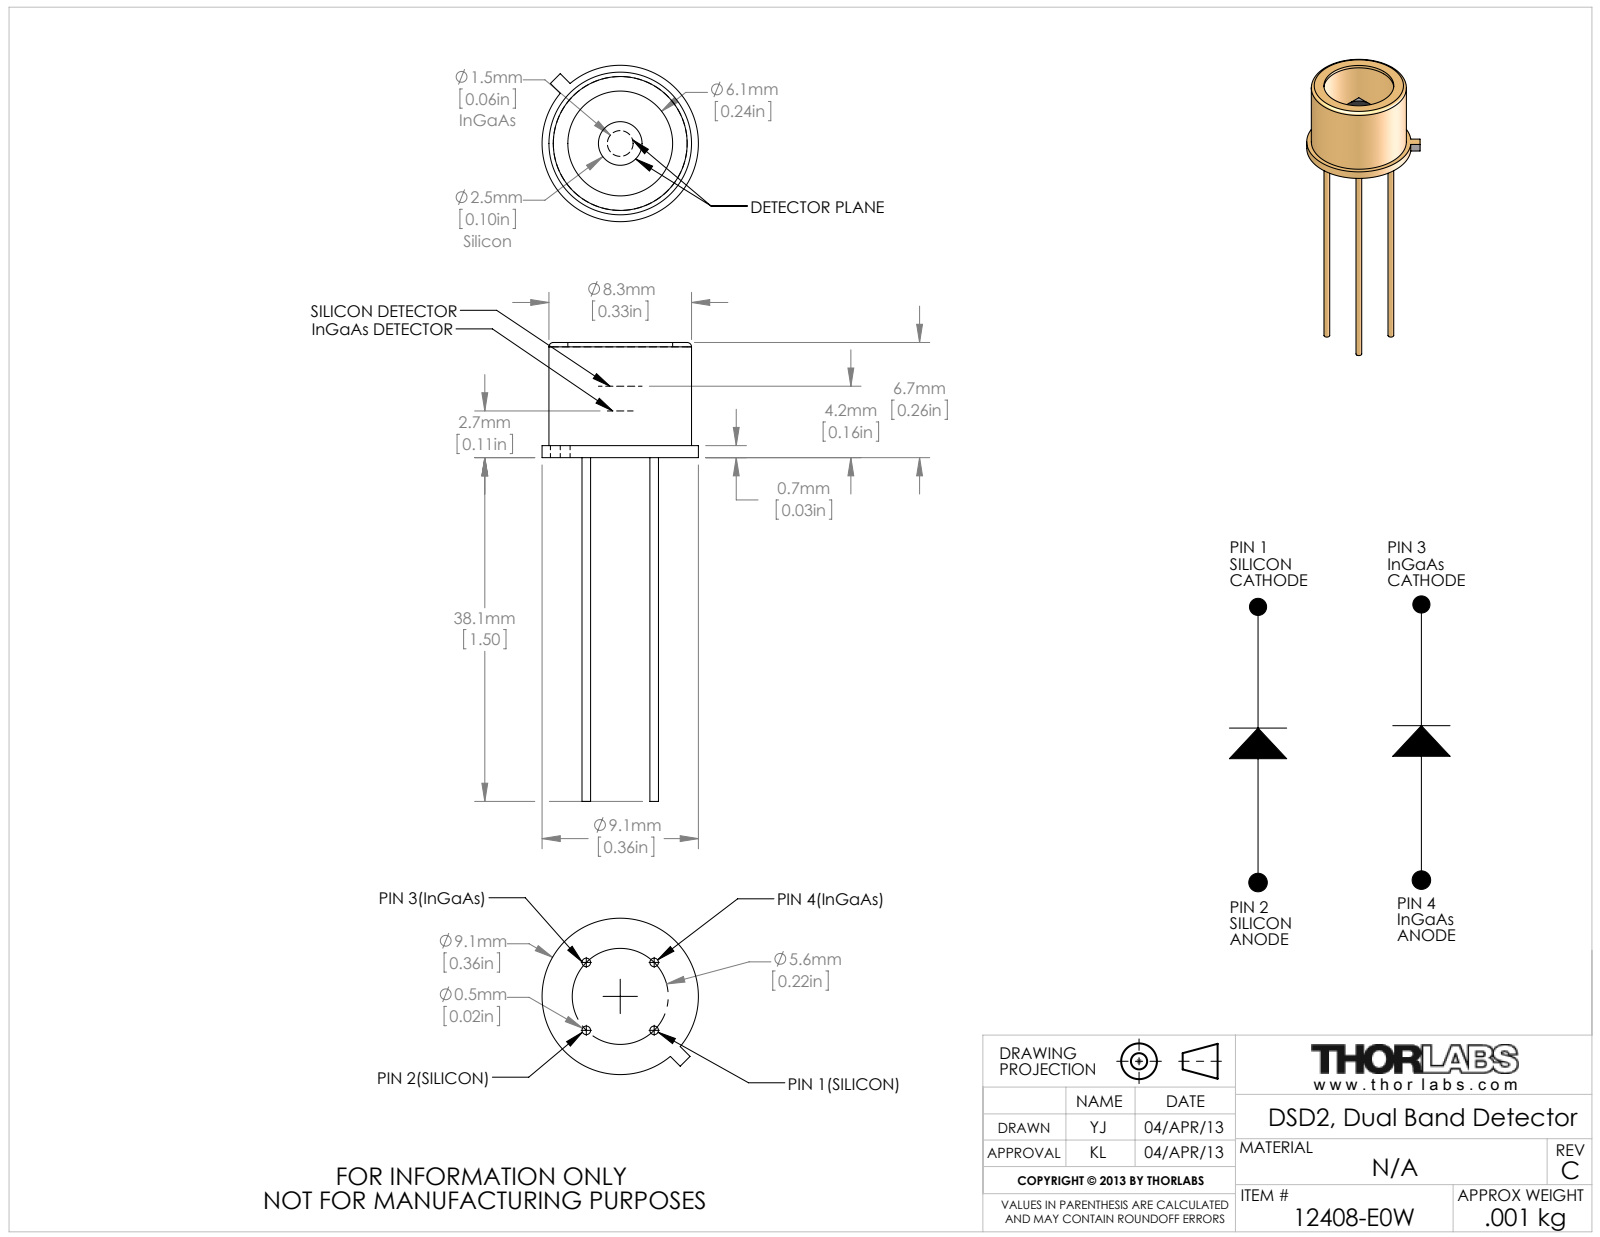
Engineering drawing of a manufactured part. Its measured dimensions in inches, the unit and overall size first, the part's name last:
Units: inches
Overall size (bounding box): 1.051 × 0.358 × 0.358
Round holes (diameter × count): ⌀0.24 ×1, ⌀0.307 ×1
Round bosses / shafts (diameter × count): ⌀0.02 ×4, ⌀0.358 ×1, ⌀0.327 ×1, ⌀0.1 ×1, ⌀0.059 ×1
Main face-to-face distances: 0.018, 0.236, 0.254, 0.264, 0.246, 0.028, 0.226, 0.16, 0.142, 0.132
Volume: 0.006 in³ · Surface area: 0.994 in²
Bodies: 3 solids, 49 faces (26 planar, 21 cylindrical, 2 other)
Part name (STEP PRODUCT): 12408-E0W
STEP written by: SolidWorks 2012 (AUTOMOTIVE_DESIGN)
